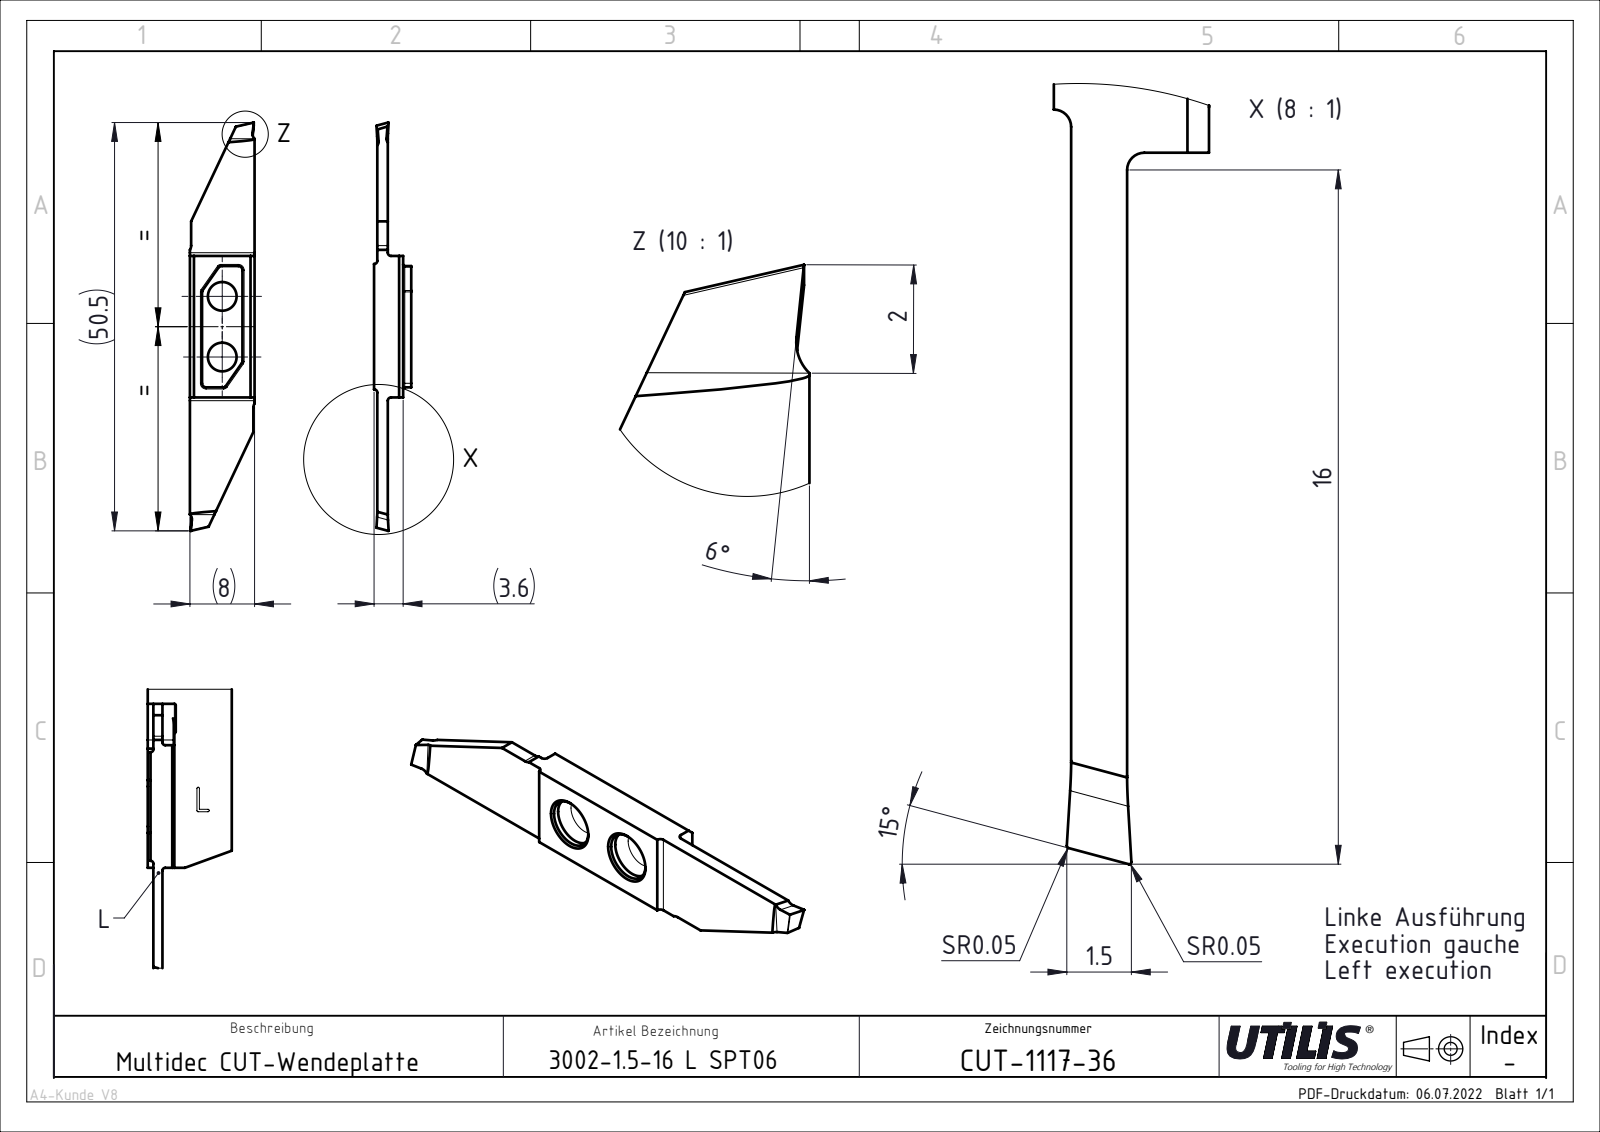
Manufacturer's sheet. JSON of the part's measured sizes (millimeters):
{"part_name": "CUT-1117; ASME Y14.5", "step_written_by": "FormatWorks Professional (AP242_MANAGED_MODEL_BASED_3D_ENGINEERING_MIM_LF)", "units": "millimeters", "bodies": {"solids": 1, "faces": 40, "planar": 24, "cylindrical": 16, "other": 0}, "overall_size": [50.5, 8, 3.6], "volume_mm3": 668, "surface_area_mm2": 937, "round_holes": [[3.55, 2]], "partial_cylinders_radius": [[0.4, 4], [1, 2]], "face_to_face_distances": [1.3, 0.4, 1.7, 3.6, 3.2, 1.9, 8, 18.09, 17.5, 7.85], "hole_center_spacings": [7.5]}
